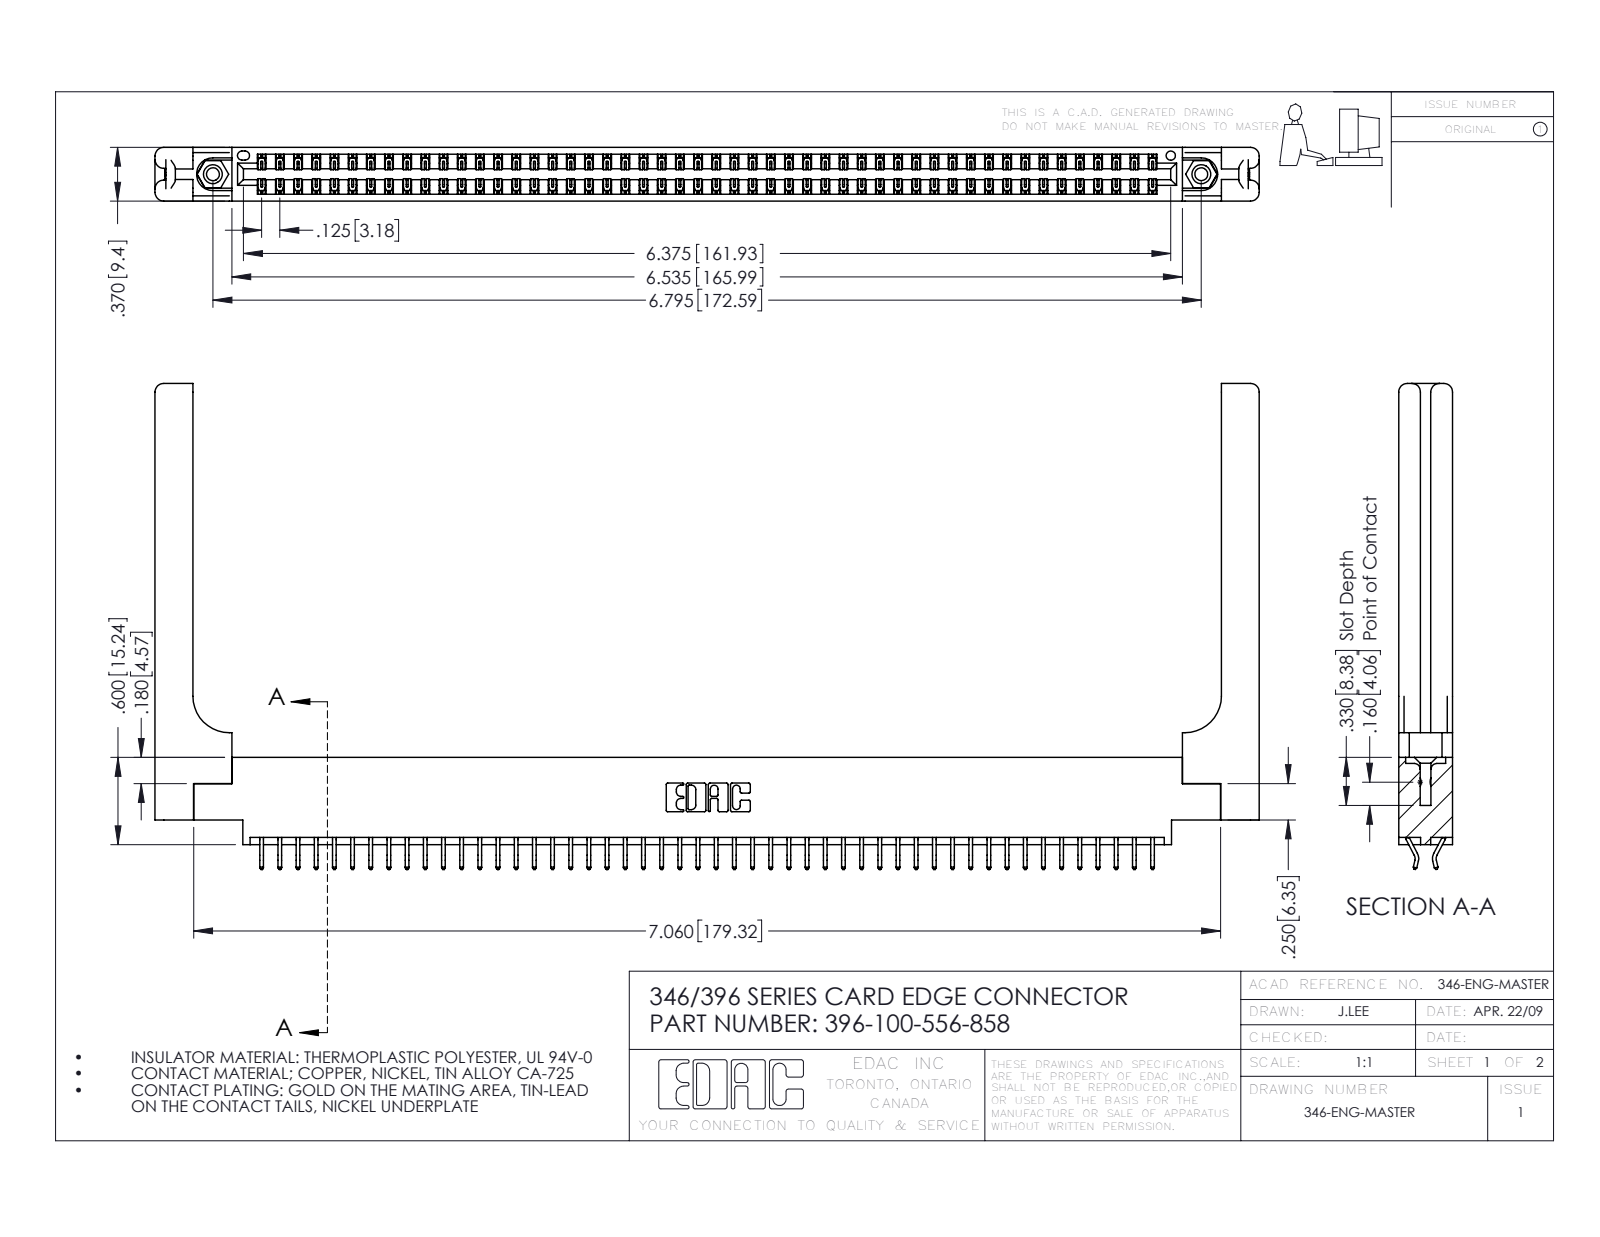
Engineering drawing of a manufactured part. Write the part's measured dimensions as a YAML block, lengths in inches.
part_name: "345-250-001_345-250-001-102; 346-220-058_345-220-058; 396-100-556-858; 345-292-001_556 Tail (+1 more)"
step_written_by: "SolidWorks 2016 (CONFIG_CONTROL_DESIGN)"
units: inches
bodies: {solids: 105, faces: 6182, planar: 4128, cylindrical: 1994, other: 60}
overall_size: [7.591, 3.34, 0.37]
volume: 1.599
surface_area: 47.89
round_holes:
  - {diameter: 0.089, count: 2}
  - {diameter: 0.125, count: 2}
  - {diameter: 0.156, count: 2}
  - {diameter: 0.064, count: 1}
round_bosses_or_shafts:
  - {diameter: 0.155, count: 2}
partial_cylinders:
  - {radius: 0.006, count: 150}
  - {radius: 0.01, count: 22}
  - {radius: 0.06, count: 16}
  - {radius: 0.007, count: 6}
  - {radius: 0.031, count: 6}
  - {radius: 0.026, count: 3}
  - {radius: 0.01, count: 2}
  - {radius: 0.014, count: 2}
face_to_face_distances: [0.37, 0.048, 0.322, 0.072, 0.148, 0.15, 0.25, 0.025, 0.298, 0.275]
hole_center_spacings: [0.246, 6.586, 6.795]
